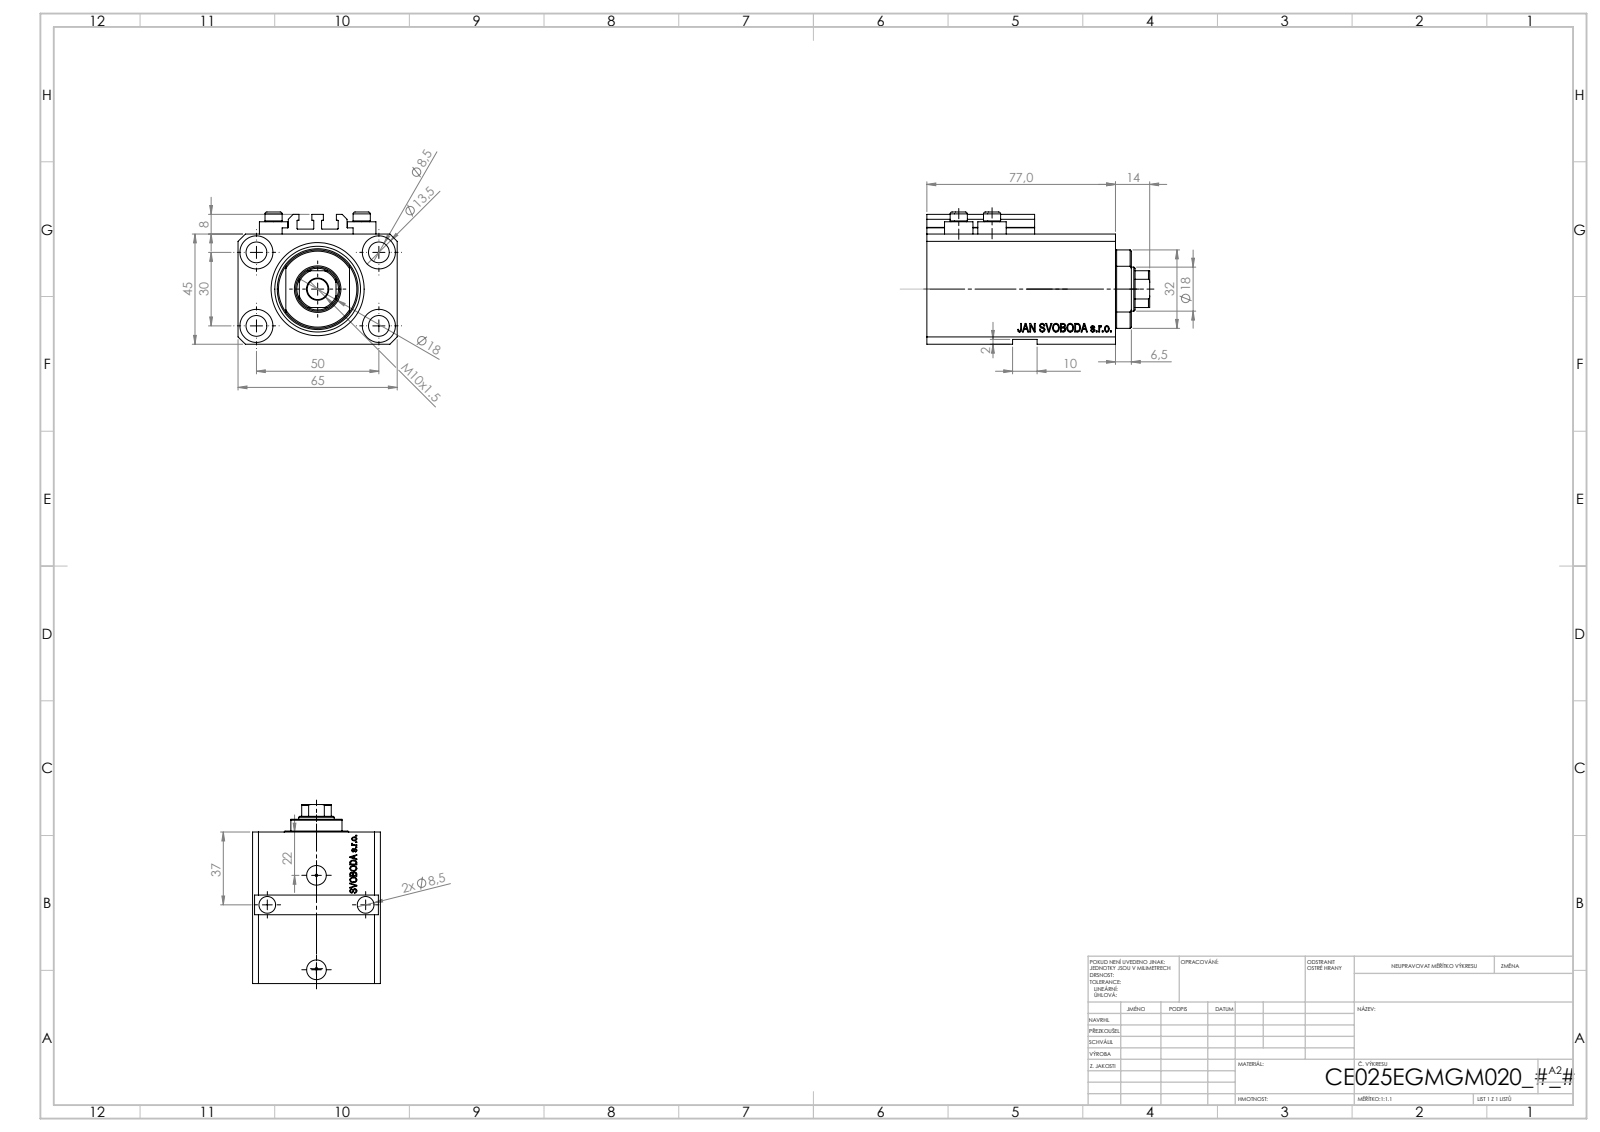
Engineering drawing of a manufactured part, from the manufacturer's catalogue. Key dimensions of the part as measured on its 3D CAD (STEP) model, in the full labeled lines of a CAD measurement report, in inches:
Part name (STEP PRODUCT): V250CE_VC_E; ALLEN BOLT V250CE; V250CE_C_VCP; V250CE_E_Body
STEP written by: SolidWorks 2019 (CONFIG_CONTROL_DESIGN)
Units: inches
Bodies: 8 solids, 1067 faces (511 planar, 126 cylindrical, 430 other)
Overall size (bounding box): 3.583 × 2.559 × 2.126
Volume: 12.19 in³ · Surface area: 91.74 in²
Round holes (diameter × count): ⌀0.335 ×7, ⌀0.049 ×4, ⌀0.157 ×4, ⌀0.531 ×4, ⌀0.394 ×2, ⌀0.518 ×2, ⌀0.787 ×2, ⌀0.709 ×1, ⌀0.984 ×1, ⌀1.496 ×1
Round bosses / shafts (diameter × count): ⌀0.457 ×4, ⌀0.276 ×4
Partial cylindrical surfaces — rounded edges, fillets, slot ends (radius × count): R0.008 ×10, R0.335 ×1, R0.63 ×1
Main face-to-face distances: 1.772, 2.559, 2.48, 0.551, 3.031, 0.079, 0.272, 2.209, 2.76, 1.85
Hole centre spacings: 1.148, 1.969, 0.535, 0.595, 0.741, 0.747, 1.032, 1.048
